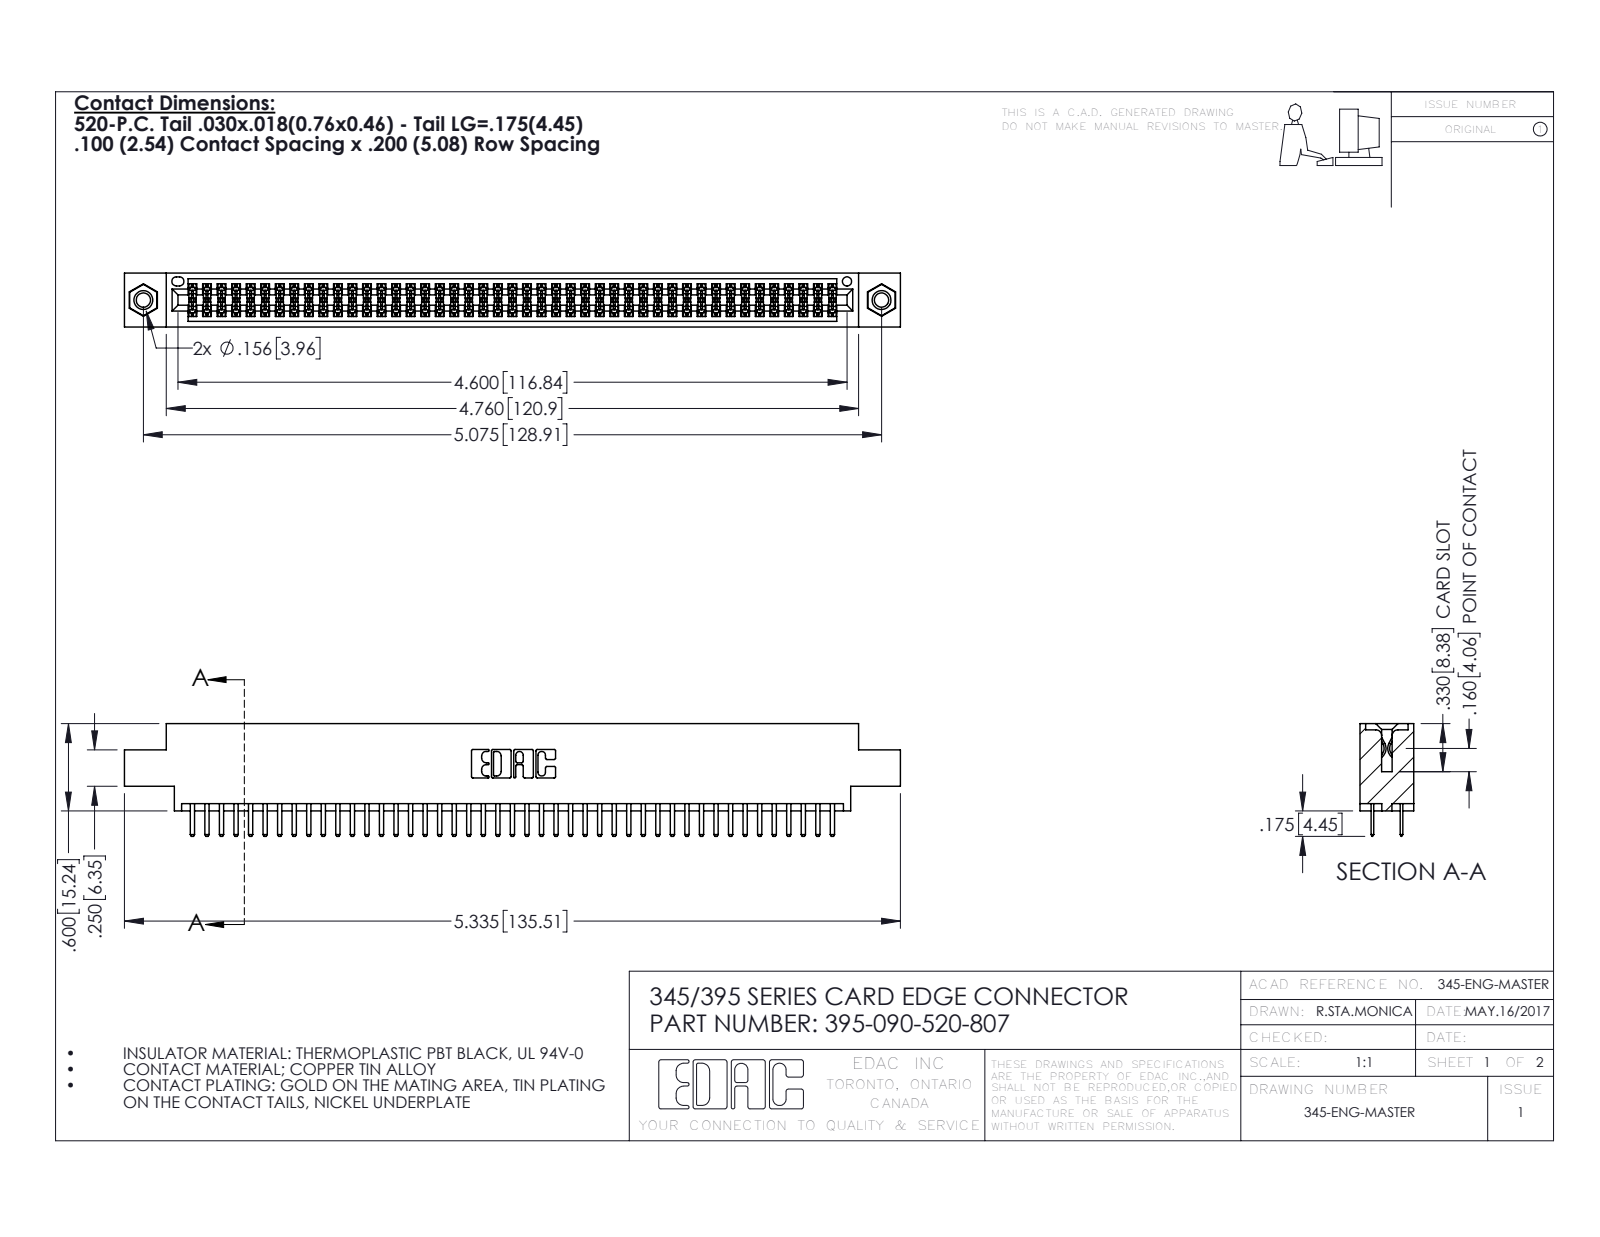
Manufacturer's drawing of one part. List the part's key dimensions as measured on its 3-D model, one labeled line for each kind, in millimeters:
Part name (STEP PRODUCT): 395-090-520-807; 345-292-001_345-293-120; 345-250-001_345-250-005-103; 345 Part_0.170 Offset - 0.156 Dia-TI
STEP written by: SolidWorks 2016 (CONFIG_CONTROL_DESIGN)
Units: millimetres
Bodies: 93 solids, 5050 faces (3266 planar, 1768 cylindrical, 16 other)
Overall size (bounding box): 135.5 × 19.7 × 9.4
Volume: 13 000 mm³ · Surface area: 19 400 mm²
Round holes (diameter × count): ⌀2.5 ×2, ⌀3.2 ×2, ⌀4 ×2, ⌀1.6 ×1
Round bosses / shafts (diameter × count): ⌀3.9 ×2
Partial cylindrical surfaces — rounded edges, fillets, slot ends (radius × count): R0.2 ×135, R0.3 ×94, R0.3 ×22, R0.2 ×6, R0.8 ×6, R0.7 ×3, R0.4 ×2, R0.5 ×2
Main face-to-face distances: 1.8, 7.6, 5.1, 9.4, 2.5, 6.9, 0.6, 5.7, 0.6, 1.8
Hole centre spacings: 6.9, 122.9, 128.9
